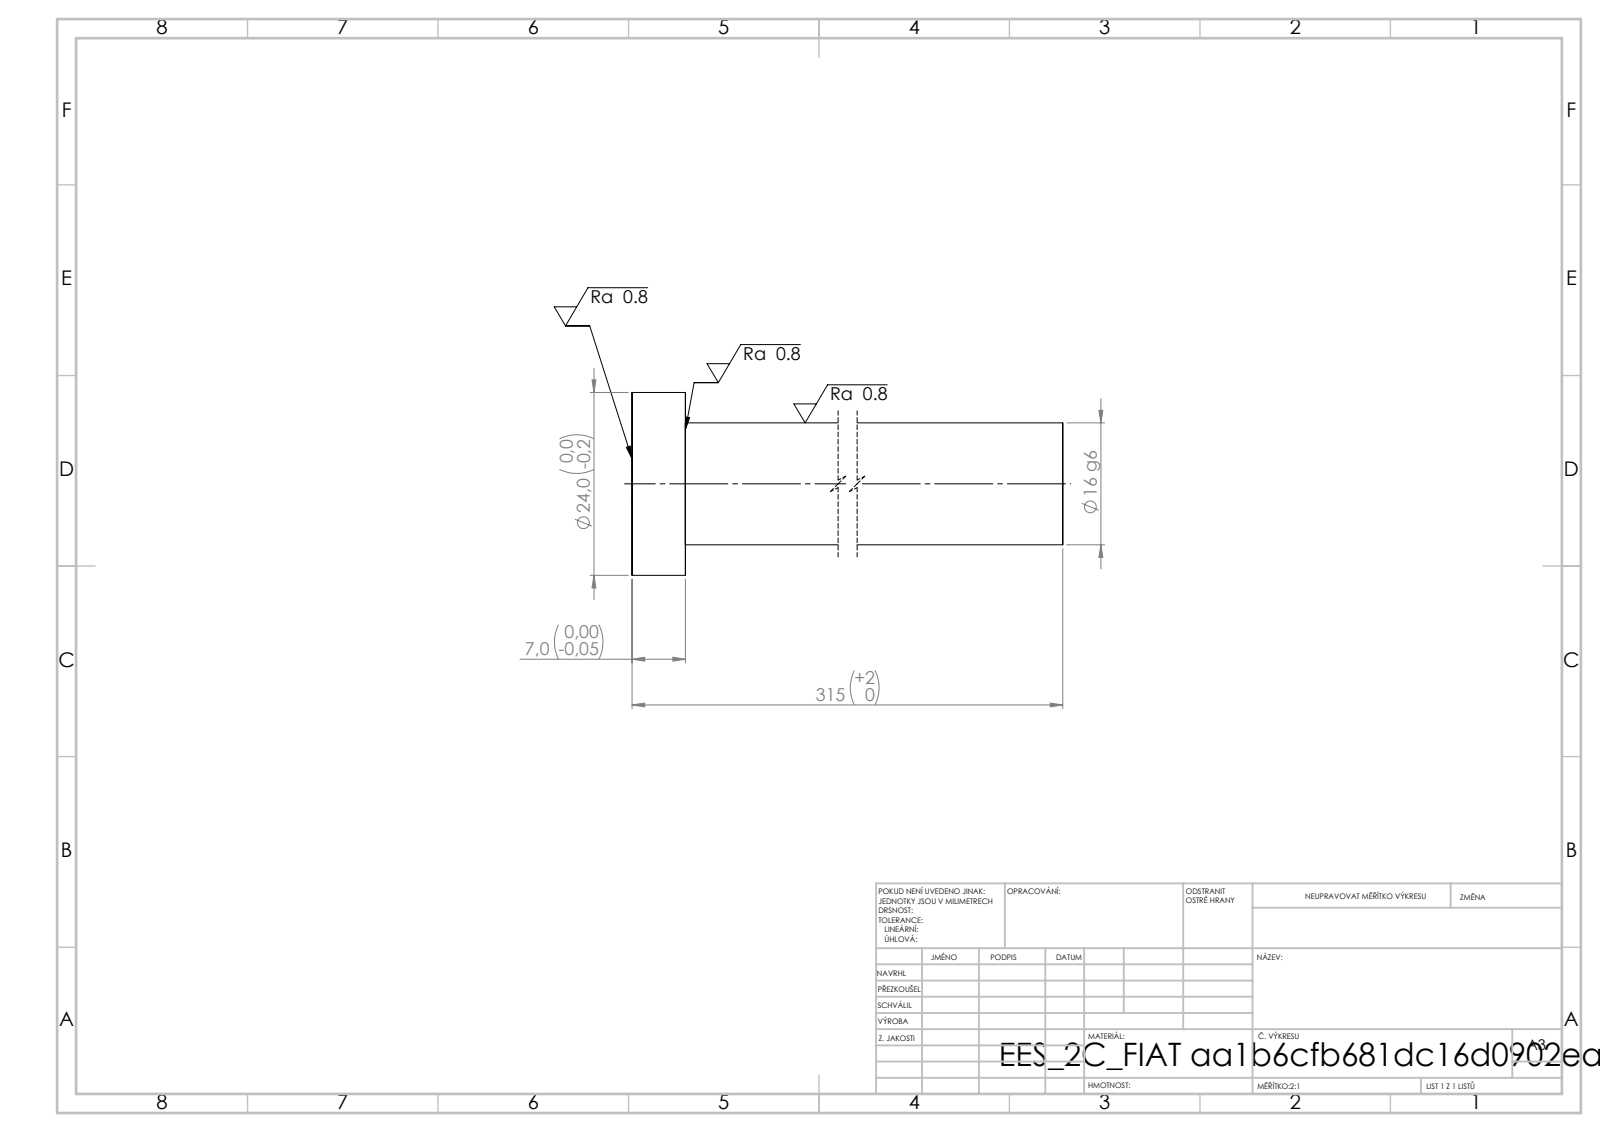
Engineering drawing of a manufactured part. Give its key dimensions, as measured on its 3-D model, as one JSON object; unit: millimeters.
{"step_written_by": "SolidWorks 2019 (CONFIG_CONTROL_DESIGN)", "units": "millimeters", "bodies": {"solids": 1, "faces": 7, "planar": 3, "cylindrical": 4, "other": 0}, "overall_size": [315, 24, 24], "volume_mm3": 65094, "surface_area_mm2": 16914, "round_bosses_or_shafts": [[24, 1], [16, 1]], "face_to_face_distances": [7, 315, 308]}
